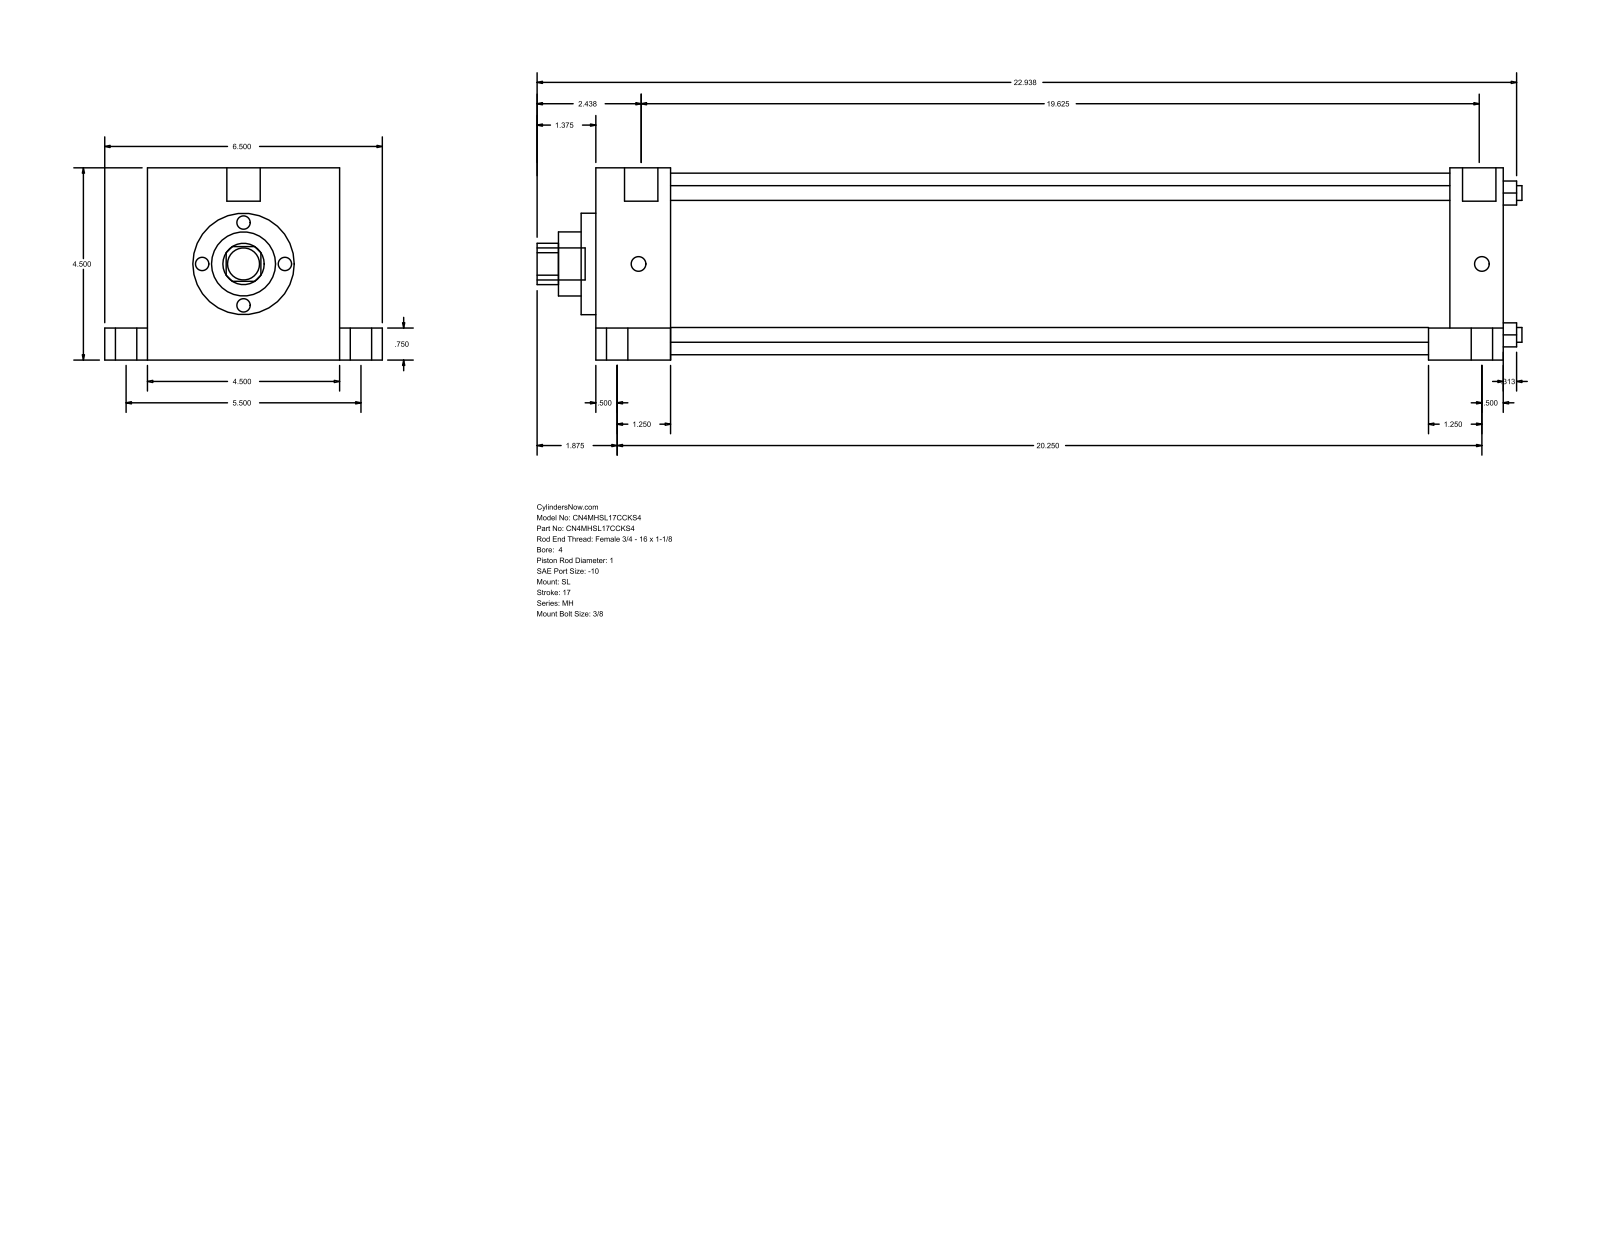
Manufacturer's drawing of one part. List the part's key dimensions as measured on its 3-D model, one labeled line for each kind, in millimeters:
Part name (STEP PRODUCT): MH_SL__0400_1
STEP written by: GSSL Pune (CONFIG_CONTROL_DESIGN)
Units: millimetres
Bodies: 0 solids, 110 faces (77 planar, 33 cylindrical, 0 other)
Overall size (bounding box): 585.79 × 165.1 × 114.3
Round holes (diameter × count): ⌀8.76 ×4, ⌀25.4 ×1, ⌀38.1 ×1, ⌀60.33 ×1, ⌀107.95 ×1
Round bosses / shafts (diameter × count): ⌀19.05 ×5, ⌀12.7 ×4, ⌀8.73 ×4, ⌀19.84 ×2
Partial cylindrical surfaces — rounded edges, fillets, slot ends (radius × count): R12.29 ×1
Main face-to-face distances: 114.3, 539.75, 44.46, 495.29, 508, 463.54, 31.75, 25.4, 139.7, 19.05
Hole centre spacings: 59.62, 84.32, 119.25
